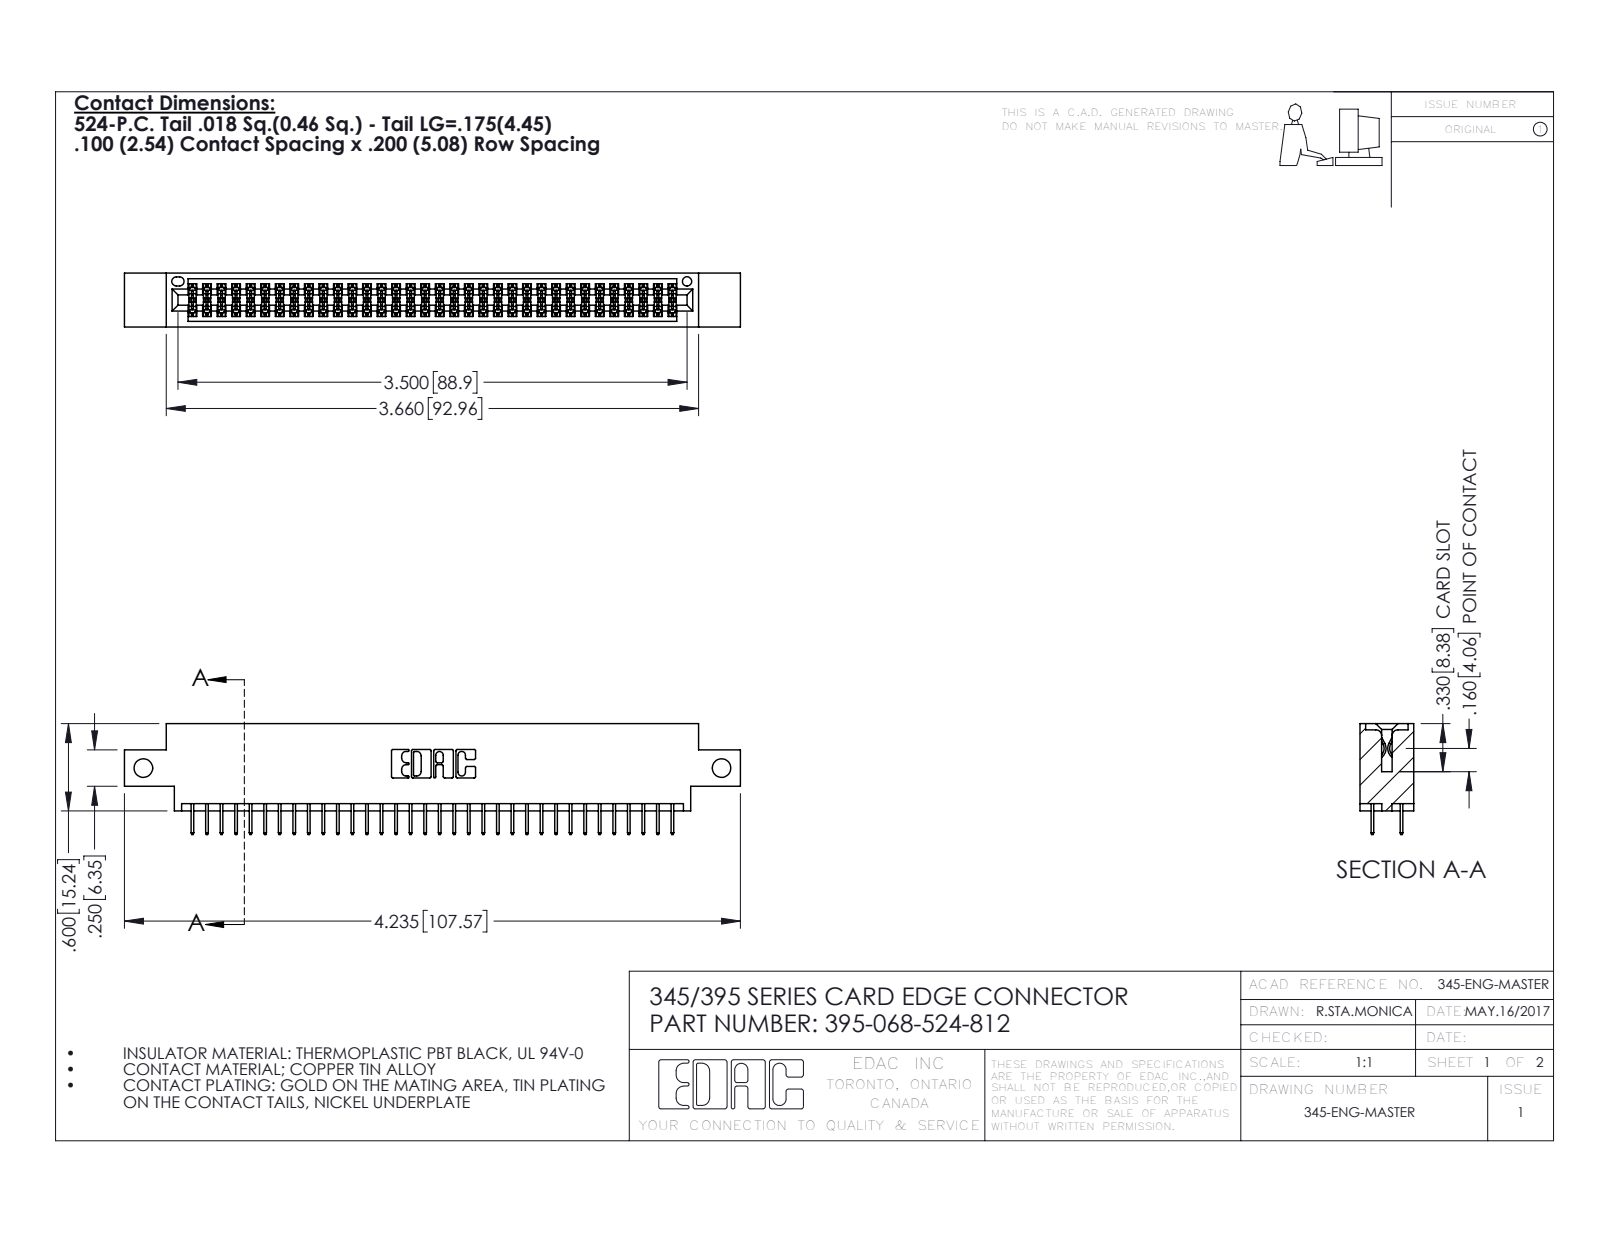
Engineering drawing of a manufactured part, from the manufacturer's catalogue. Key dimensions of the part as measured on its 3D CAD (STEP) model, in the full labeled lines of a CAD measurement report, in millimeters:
Part name (STEP PRODUCT): 395-068-524-812; 345-292-001_345-293-124; 345 Part_0.170 Offset - Side Mount
STEP written by: SolidWorks 2016 (CONFIG_CONTROL_DESIGN)
Units: millimetres
Bodies: 69 solids, 3802 faces (2736 planar, 1066 cylindrical, 0 other)
Overall size (bounding box): 107.6 × 19.4 × 9.4
Volume: 10 100 mm³ · Surface area: 14 470 mm²
Round holes (diameter × count): ⌀3.3 ×2, ⌀1.6 ×1
Partial cylindrical surfaces — rounded edges, fillets, slot ends (radius × count): R0.2 ×102, R0.3 ×22, R0.2 ×6, R0.8 ×6, R0.7 ×3, R0.4 ×2, R0.5 ×2, R0.6 ×2
Main face-to-face distances: 1.8, 7.6, 9.4, 5.1, 2.5, 6.9, 0.6, 5.7, 4.4, 1.8
Hole centre spacings: 101
